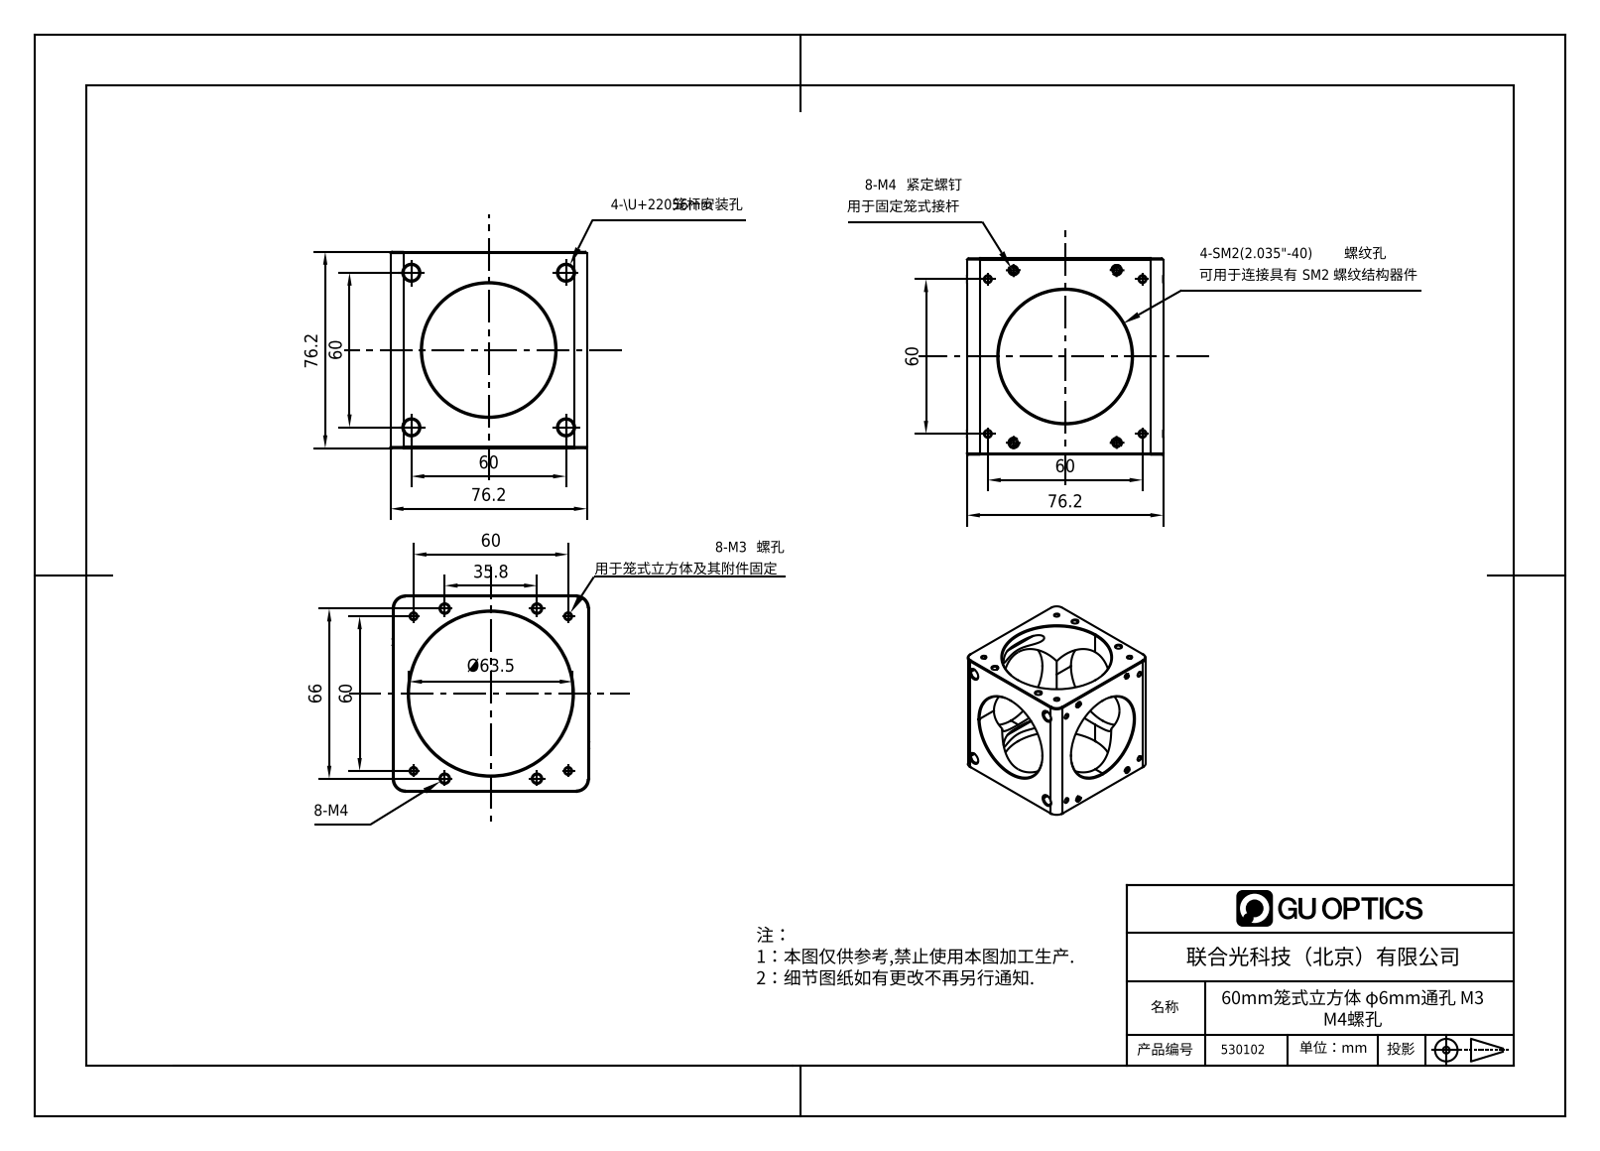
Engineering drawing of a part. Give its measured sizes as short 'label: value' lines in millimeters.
written by: SolidWorks 2018 (CONFIG_CONTROL_DESIGN)
unit: mm
bodies: 0 solids, 302 faces (70 planar, 72 cylindrical, 160 other)
size: 76.29 × 76.2 × 76.2
holes: 8× ⌀2.5, 4× ⌀3.3, 4× ⌀6, 2× ⌀51.69, 1× ⌀63.5
rounds: 4× R5
face distances: 76.2, 107.04, 2.1, 76.3, 76.25, 52.18, 24.14, 26.24, 50.08, 54.28
hole spacings: 42.43, 60, 84.85, 12.47, 37.54, 47.99, 64.15, 79.14
